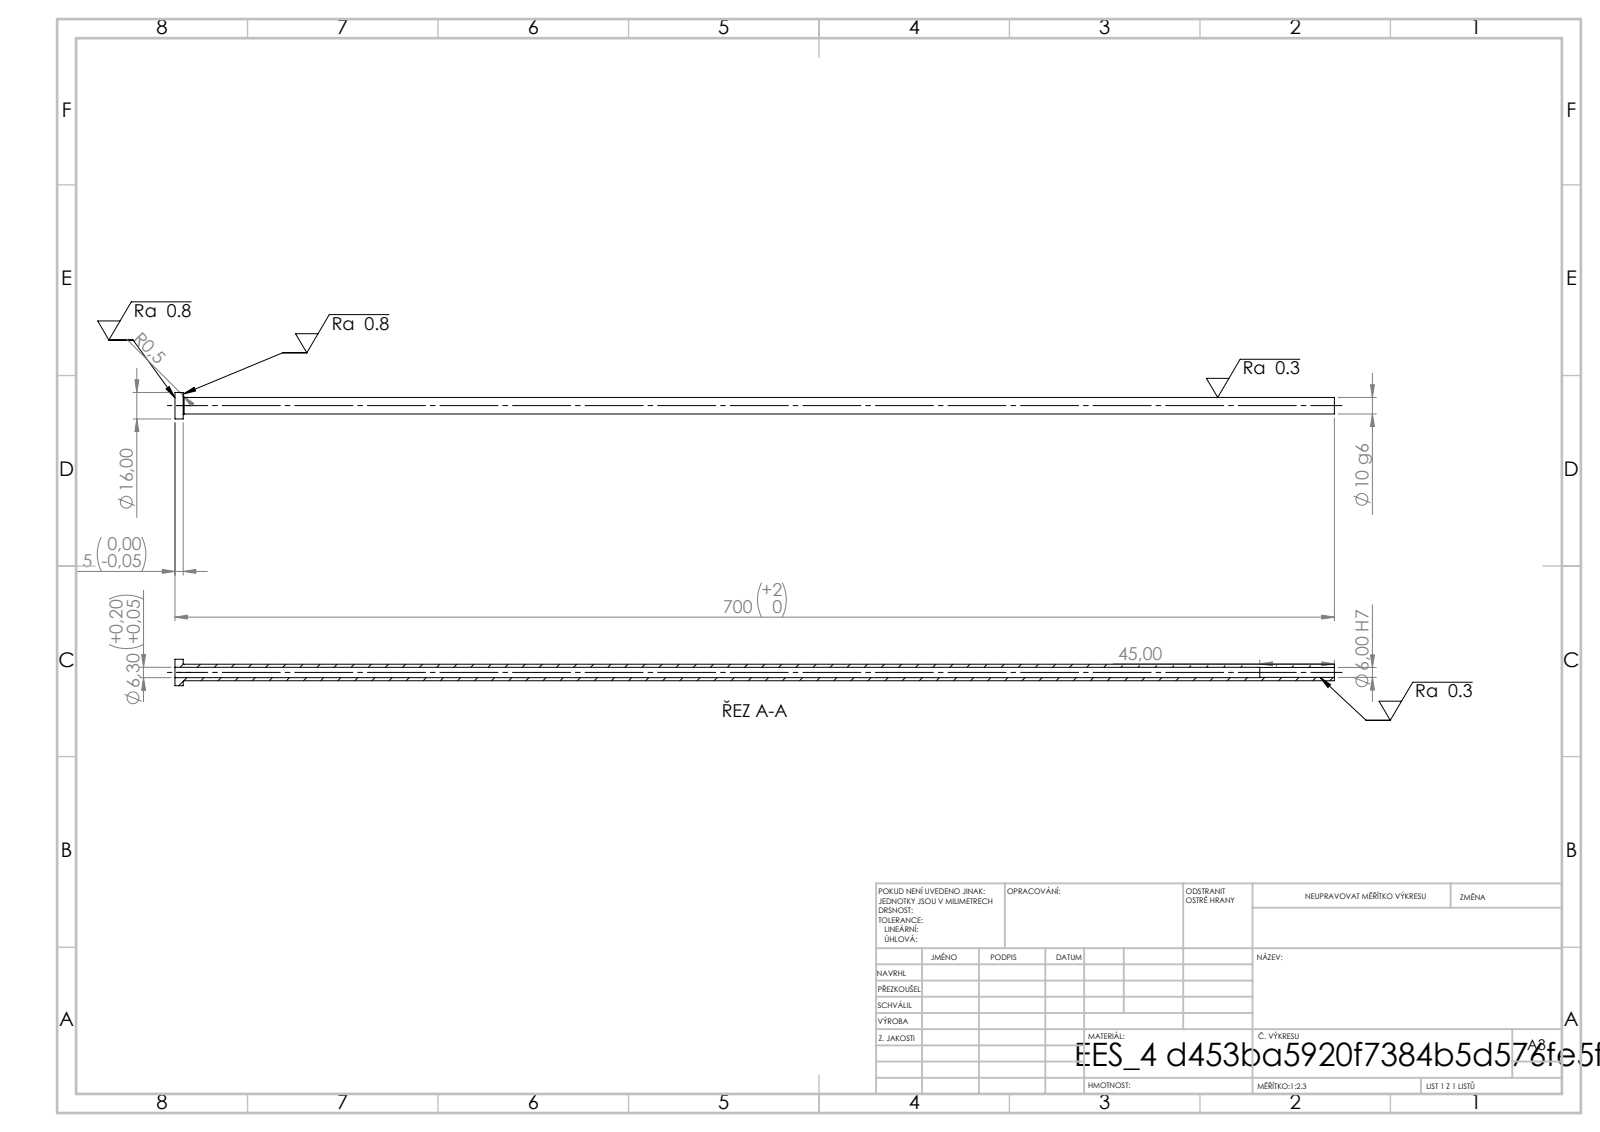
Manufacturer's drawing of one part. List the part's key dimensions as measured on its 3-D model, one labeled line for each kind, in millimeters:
STEP written by: SolidWorks 2019 (CONFIG_CONTROL_DESIGN)
Units: millimetres
Bodies: 1 solid, 14 faces (4 planar, 8 cylindrical, 2 other)
Overall size (bounding box): 700 × 16 × 16
Volume: 33 902 mm³ · Surface area: 36 236 mm²
Round holes (diameter × count): ⌀6 ×1, ⌀6.3 ×1
Round bosses / shafts (diameter × count): ⌀16 ×1, ⌀10 ×1
Main face-to-face distances: 5, 700, 695, 655, 650, 45
